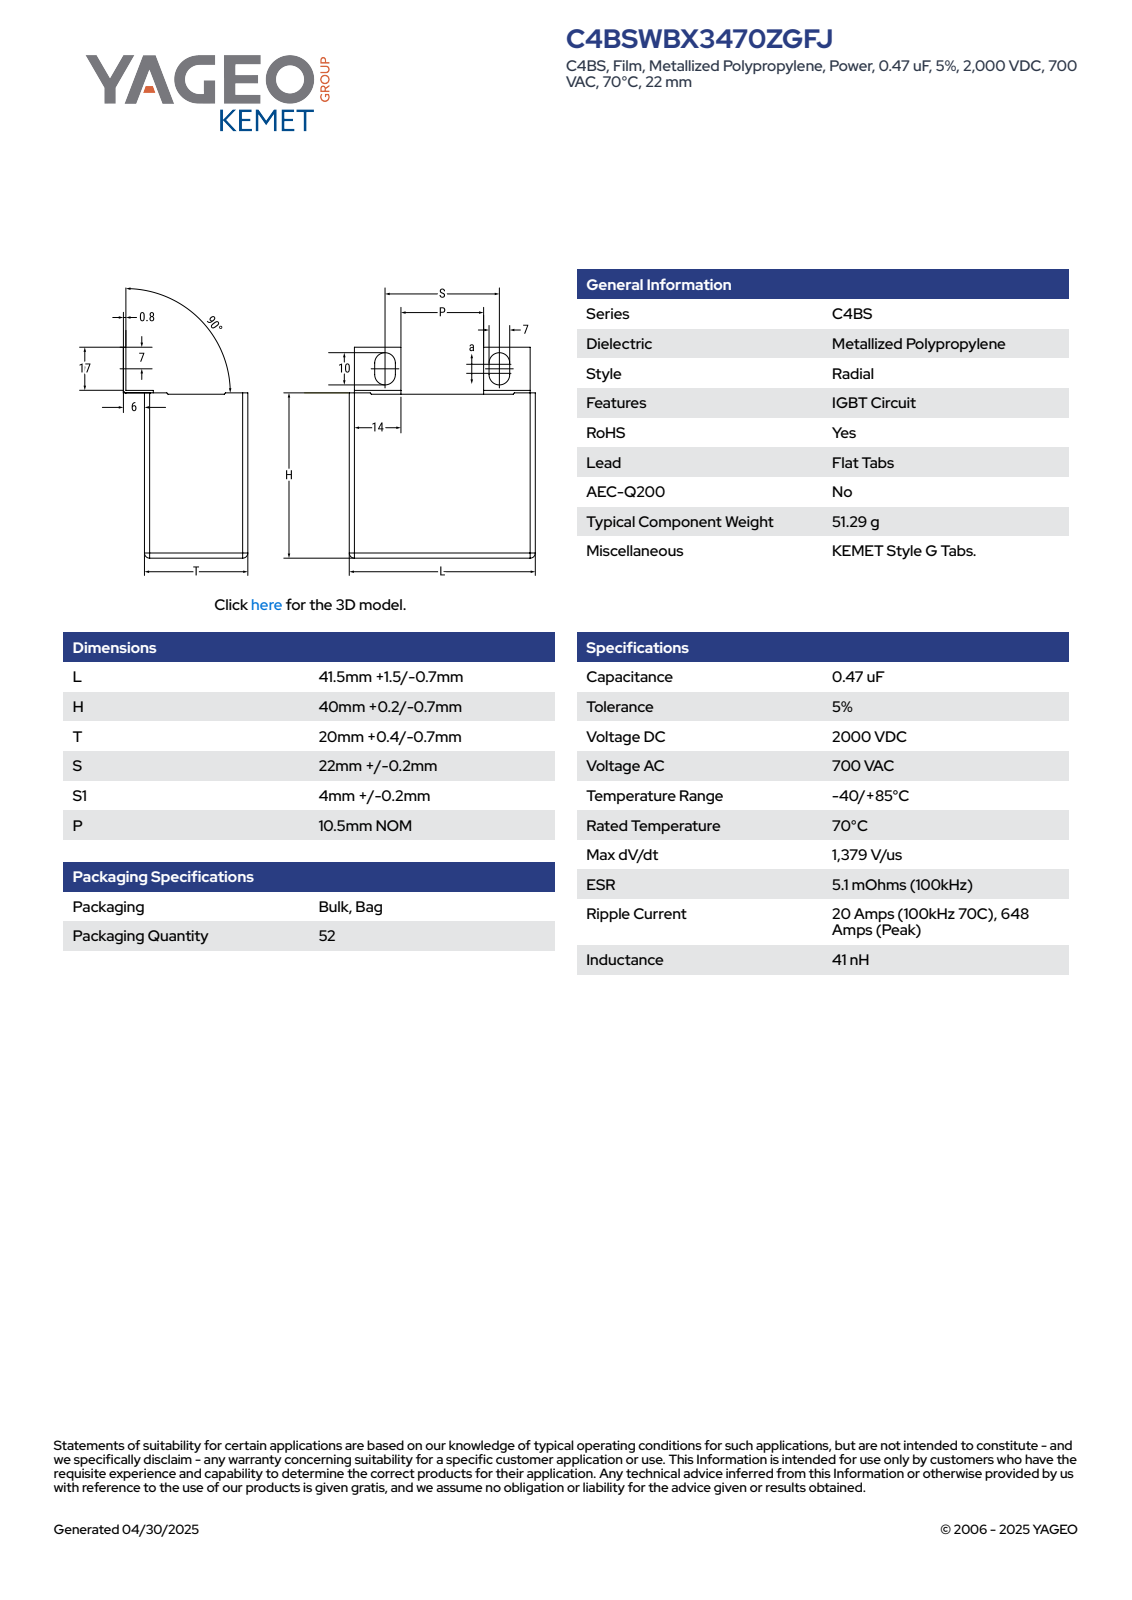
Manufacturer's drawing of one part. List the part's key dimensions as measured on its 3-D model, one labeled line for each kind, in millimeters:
Part name (STEP PRODUCT): CFP_C4BG_41.5X40X20_L43H40.2T20.4S22.02
STEP written by: SolidWorks 2014 (AUTOMOTIVE_DESIGN)
Units: millimetres
Bodies: 4 solids, 93 faces (79 planar, 14 cylindrical, 0 other)
Overall size (bounding box): 57.2 × 43 × 27.05
Volume: 35 672 mm³ · Surface area: 8 157 mm²
Partial cylindrical surfaces — rounded edges, fillets, slot ends (radius × count): R3.97 ×4, R8.02 ×4, R0.5 ×2
Main face-to-face distances: 20.4, 40.2, 43, 0.6, 6.65, 27.05, 6.05, 26.45, 40.8, 2.25
